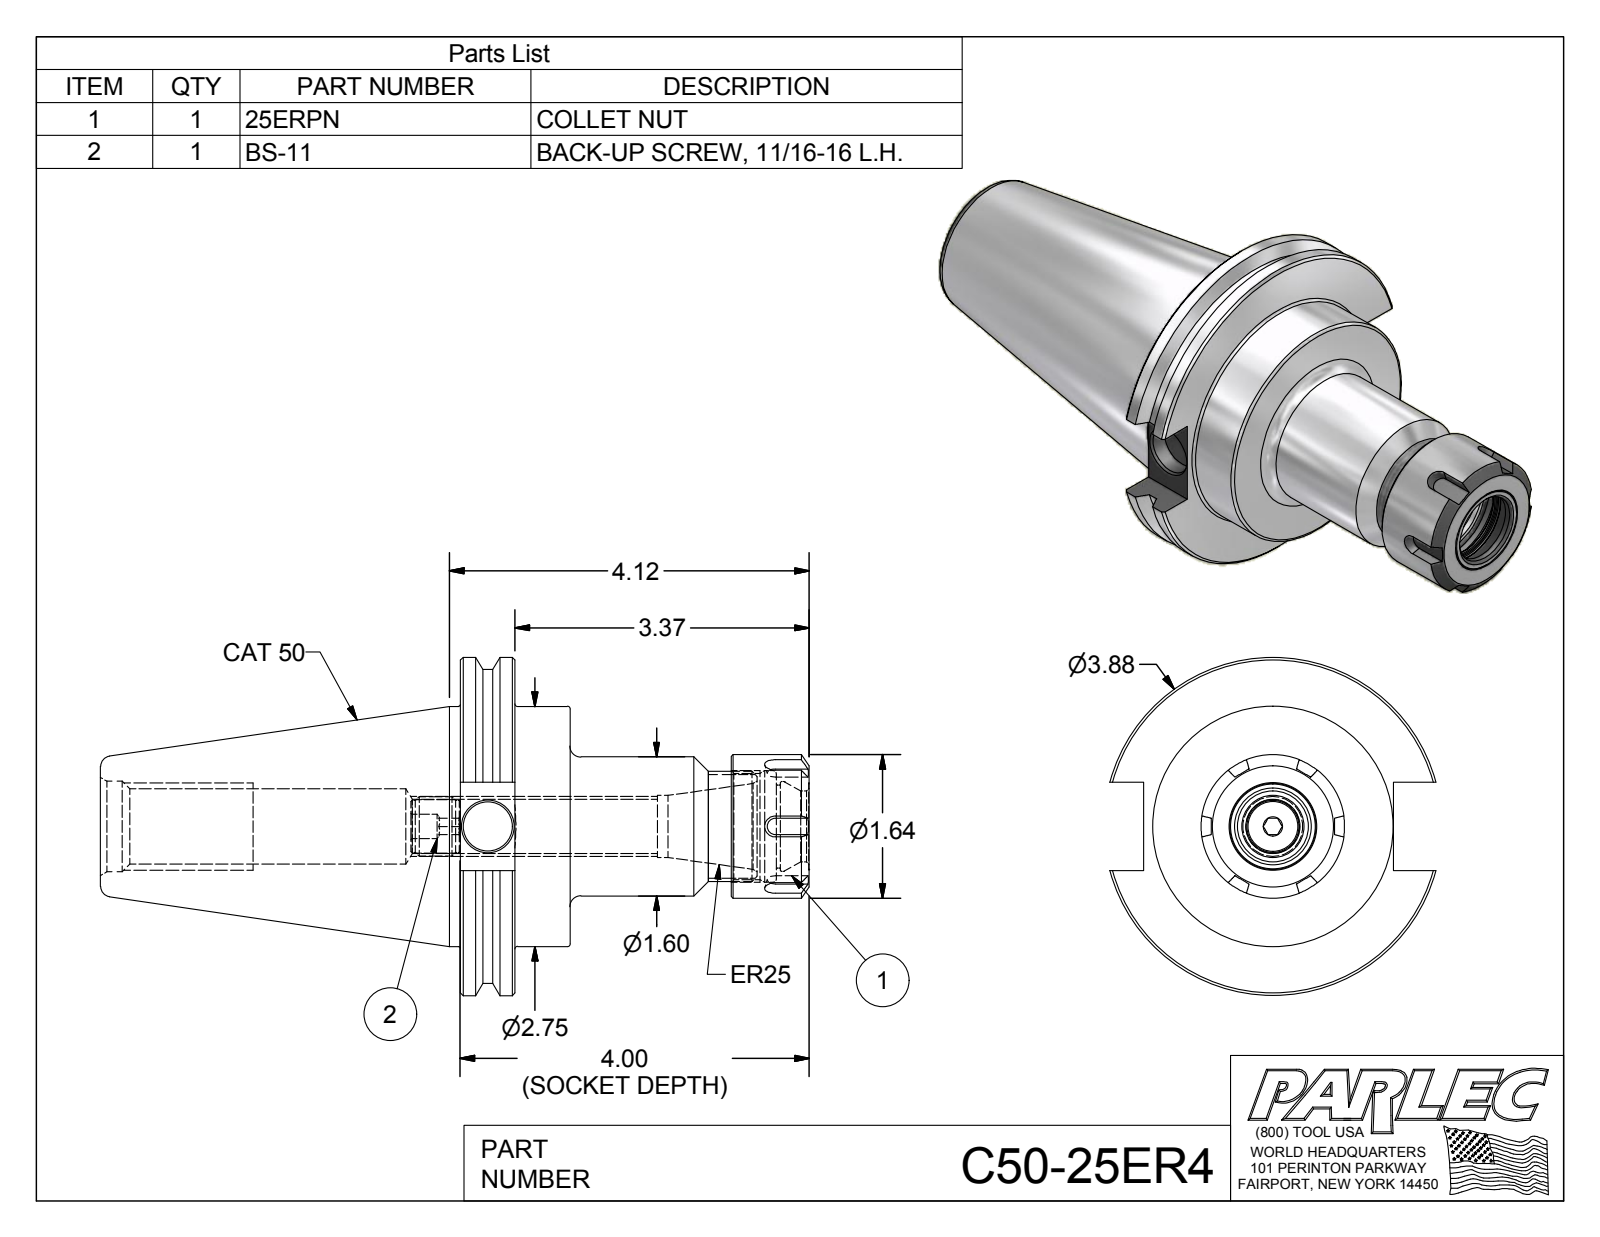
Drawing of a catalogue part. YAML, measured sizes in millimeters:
part_name: "C50-25ER4; C50-25ER4-1; 25ERPN; BS-11"
step_written_by: "Autodesk Inventor 2012 (AUTOMOTIVE_DESIGN)"
units: millimeters
bodies: {solids: 3, faces: 117, planar: 43, cylindrical: 25, other: 49}
overall_size: [206.2, 98.4, 95]
volume: 446400
surface_area: 64770
round_holes:
  - {diameter: 7.1, count: 1}
  - {diameter: 14.3, count: 1}
  - {diameter: 15.7, count: 1}
  - {diameter: 18, count: 1}
  - {diameter: 20.6, count: 1}
  - {diameter: 22, count: 1}
  - {diameter: 24.1, count: 1}
  - {diameter: 26.1, count: 1}
  - {diameter: 26.4, count: 1}
  - {diameter: 30.9, count: 1}
  - {diameter: 32.5, count: 1}
round_bosses_or_shafts:
  - {diameter: 98.4, count: 1}
  - {diameter: 91.3, count: 1}
  - {diameter: 69.9, count: 1}
  - {diameter: 41.7, count: 1}
  - {diameter: 40.5, count: 1}
  - {diameter: 32, count: 1}
  - {diameter: 17.3, count: 1}
  - {diameter: 15.1, count: 1}
face_to_face_distances: [15.9, 16, 31.9, 101.5, 85.6, 69.6, 78.8, 62.9, 46.9, 22.7]
